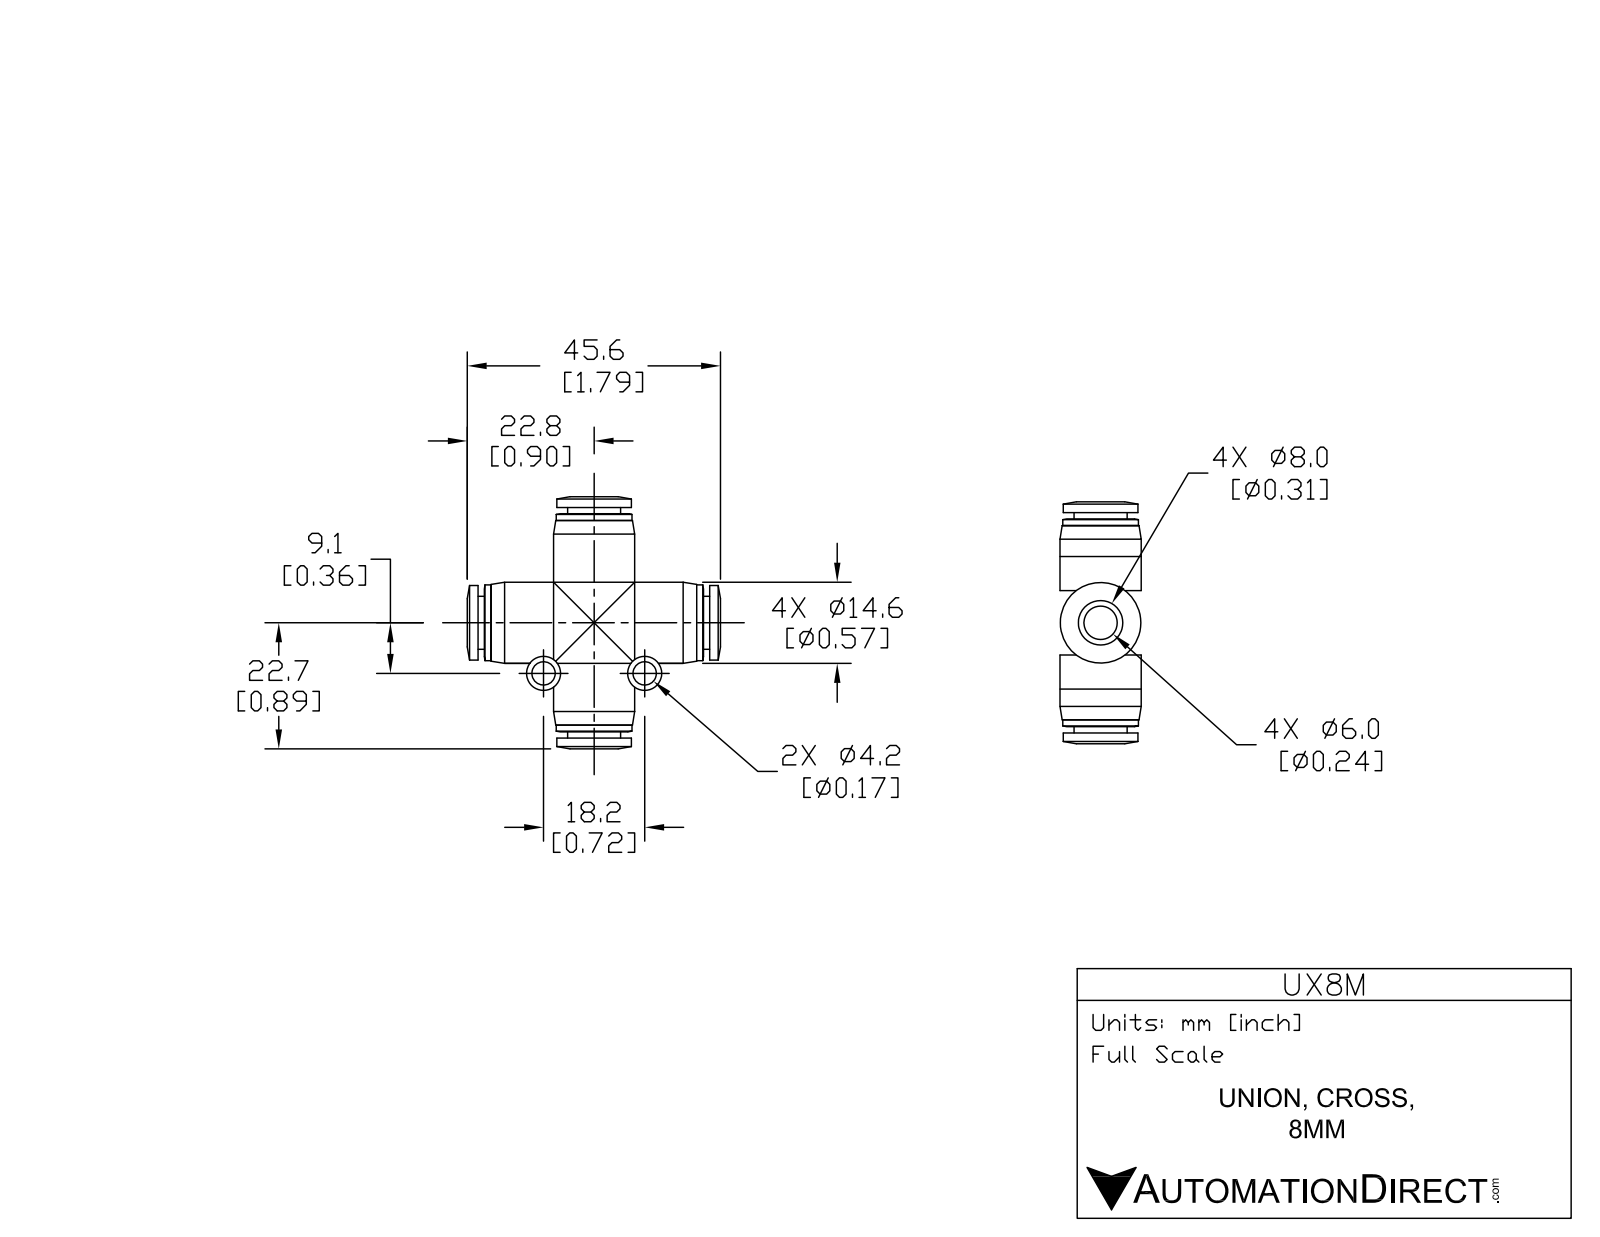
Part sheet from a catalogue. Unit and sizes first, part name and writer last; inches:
Units: inches
Overall size (bounding box): 1.834 × 1.759 × 0.591
Round holes (diameter × count): ⌀0.165 ×2, ⌀0.268 ×2, ⌀0.327 ×2
Round bosses / shafts (diameter × count): ⌀0.591 ×2, ⌀0.551 ×2, ⌀0.543 ×2, ⌀0.386 ×2, ⌀0.248 ×2
Partial cylindrical surfaces — rounded edges, fillets, slot ends (radius × count): R0.197 ×2
Main face-to-face distances: 0.045, 1.557, 1.632, 1.677, 1.602, 0.642, 0.596, 1.587, 1.512, 0.669
Hole centre spacings: 0.717
Volume: 0.502 in³ · Surface area: 11.27 in²
Bodies: 1 solid, 124 faces (28 planar, 64 cylindrical, 32 other)
Part name (STEP PRODUCT): UX8M
STEP written by: SolidWorks 2018 (AUTOMOTIVE_DESIGN)
